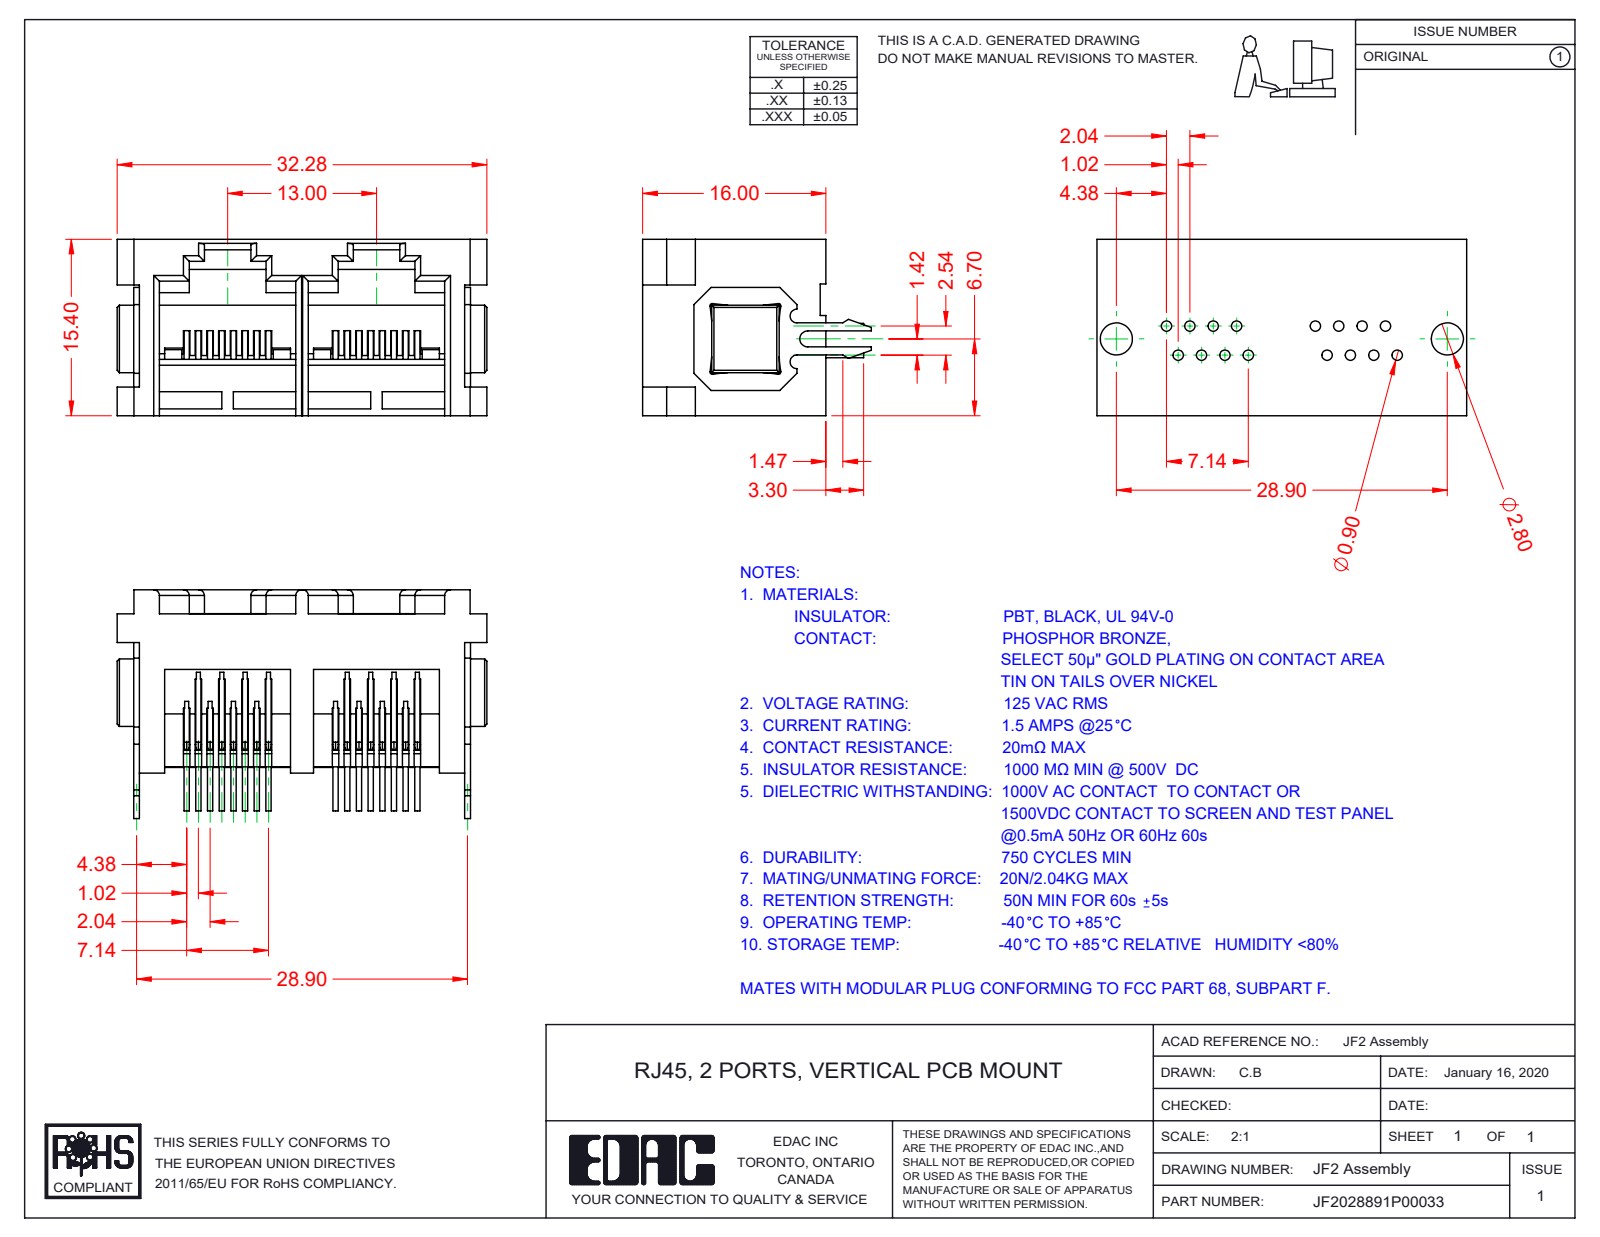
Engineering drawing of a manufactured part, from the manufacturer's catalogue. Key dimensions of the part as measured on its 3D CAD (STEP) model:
Part name (STEP PRODUCT): F2 Contacts; F2 Contact Lock; F2 Insulator; RJF2028891P00033 (+1 more)
STEP written by: SolidWorks 2016 (CONFIG_CONTROL_DESIGN)
Units: millimetres
Bodies: 21 solids, 1130 faces (734 planar, 300 cylindrical, 96 other)
Overall size (bounding box): 32.28 × 19.97 × 15.4
Volume: 3 519 mm³ · Surface area: 6 910 mm²
Round bosses / shafts (diameter × count): ⌀0.46 ×64
Partial cylindrical surfaces — rounded edges, fillets, slot ends (radius × count): R0.18 ×32, R0.5 ×15, R0.2 ×4, R20.35 ×4, R0.3 ×3, R0.6 ×2, R0.21 ×1, R0.45 ×1
Main face-to-face distances: 12.59, 2.1, 13, 1.5, 2.81, 0.92, 11.67, 0.5, 28.4, 11
